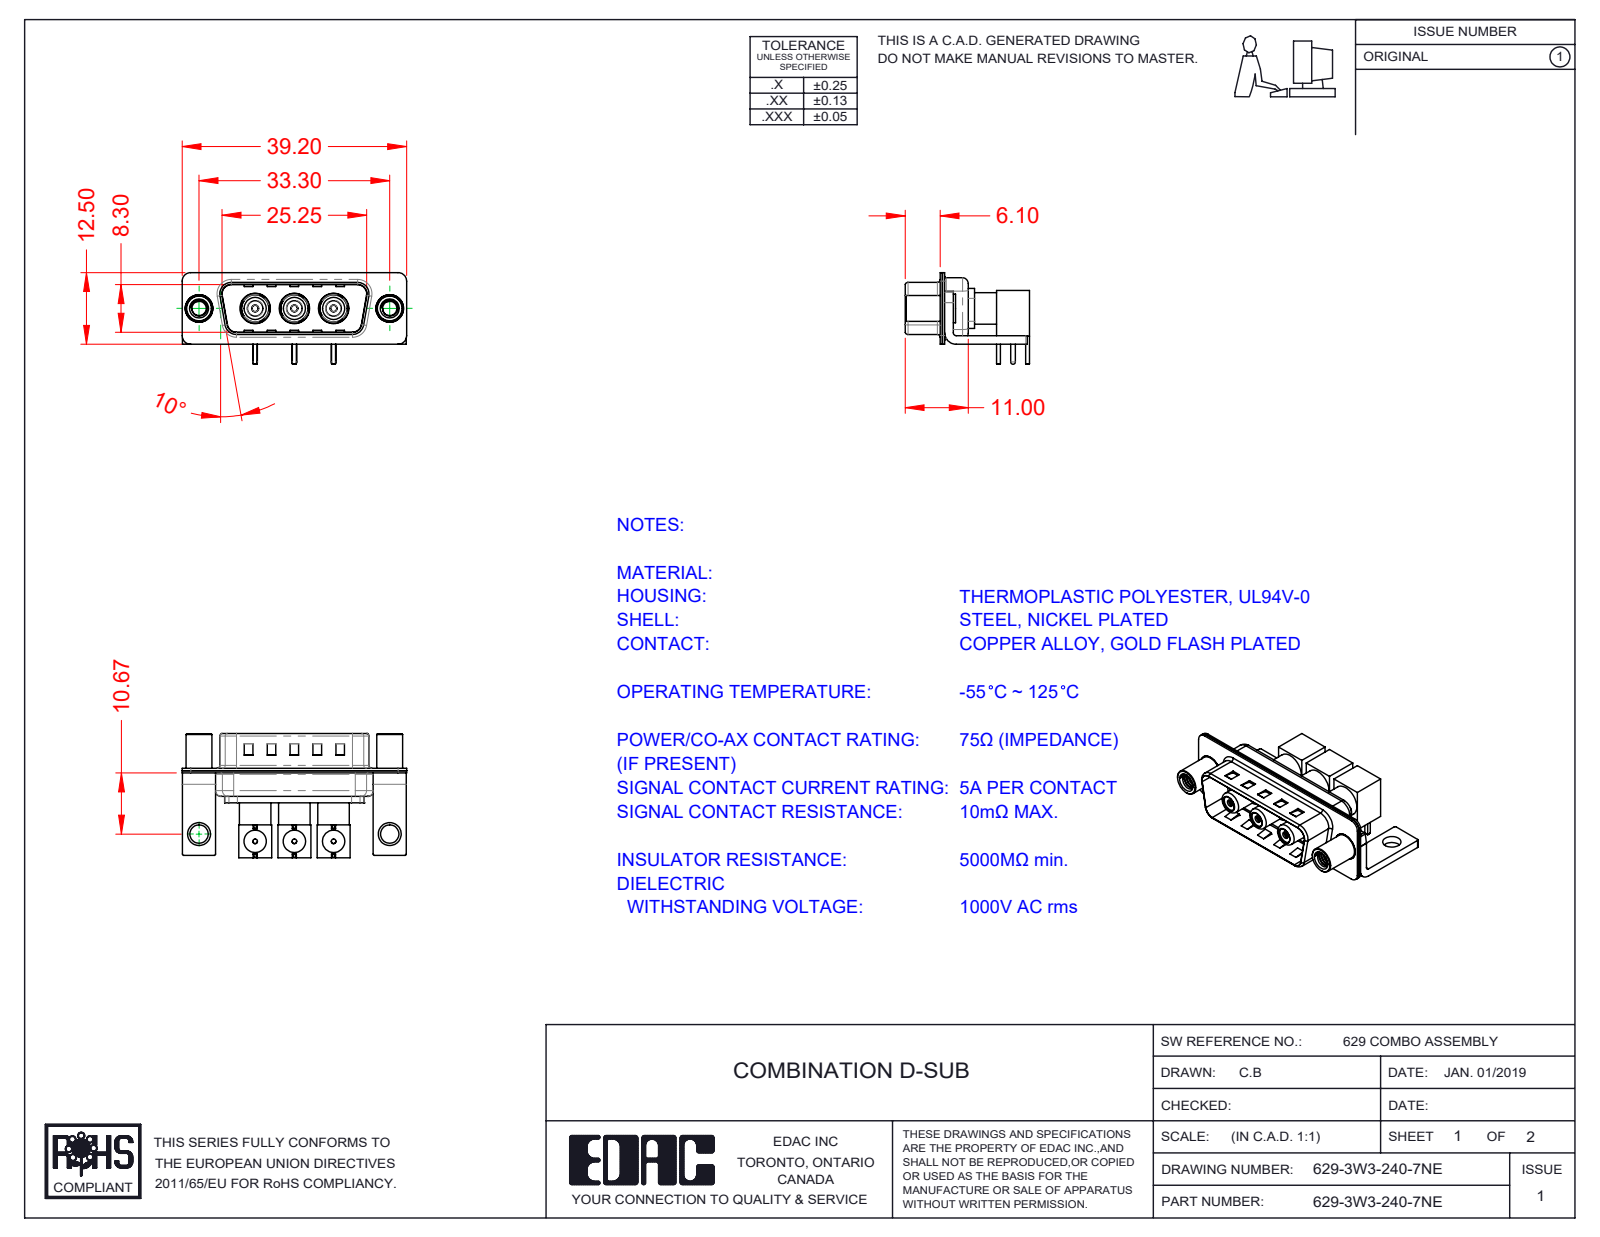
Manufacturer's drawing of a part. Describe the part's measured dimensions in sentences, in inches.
The part is named "Insulator Socket 2; RA Back Shell; Co-Ax Jack_RA PC Tail; Co-Ax Jack Assy_RA (+8 more)". Its 3-D file was written by "SolidWorks 2020 (CONFIG_CONTROL_DESIGN)". It is 28 solids with 894 faces: 332 planar, 406 cylindrical and 156 other. Overall it measures 1.543 by 0.855 by 0.63 inches. Its volume is 0.188 cubic inches and its surface area 13.09 square inches. Round holes: 5 of diameter 0.098, 3 of diameter 0.031, 3 of diameter 0.043, 3 of diameter 0.047, 3 of diameter 0.059, 3 of diameter 0.063, 3 of diameter 0.106, 3 of diameter 0.122, 3 of diameter 0.134, 3 of diameter 0.154, 3 of diameter 0.161, 3 of diameter 0.191. Round bosses or shafts: 6 of diameter 0.031, 3 of diameter 0.217, 3 of diameter 0.205, 3 of diameter 0.189, 3 of diameter 0.186, 3 of diameter 0.164, 3 of diameter 0.157, 3 of diameter 0.152. Partial cylindrical surfaces (rounded edges, fillets, slot ends): 16 of radius 0.01, 16 of radius 0.059, 13 of radius 0.079, 9 of radius 0.02, 8 of radius 0.063, 4 of radius 0.024, 4 of radius 0.026, 4 of radius 0.035. The main face-to-face distances are 0.016, 0.031, 0.059, 0.226, 0.374, 0.055, 0.358, 0.343, 0.043, 0.014. The hole center spacings are 0.27, 0.539, 0.389, 0.657, 0.926, 0.386, 0.656, 0.925.
